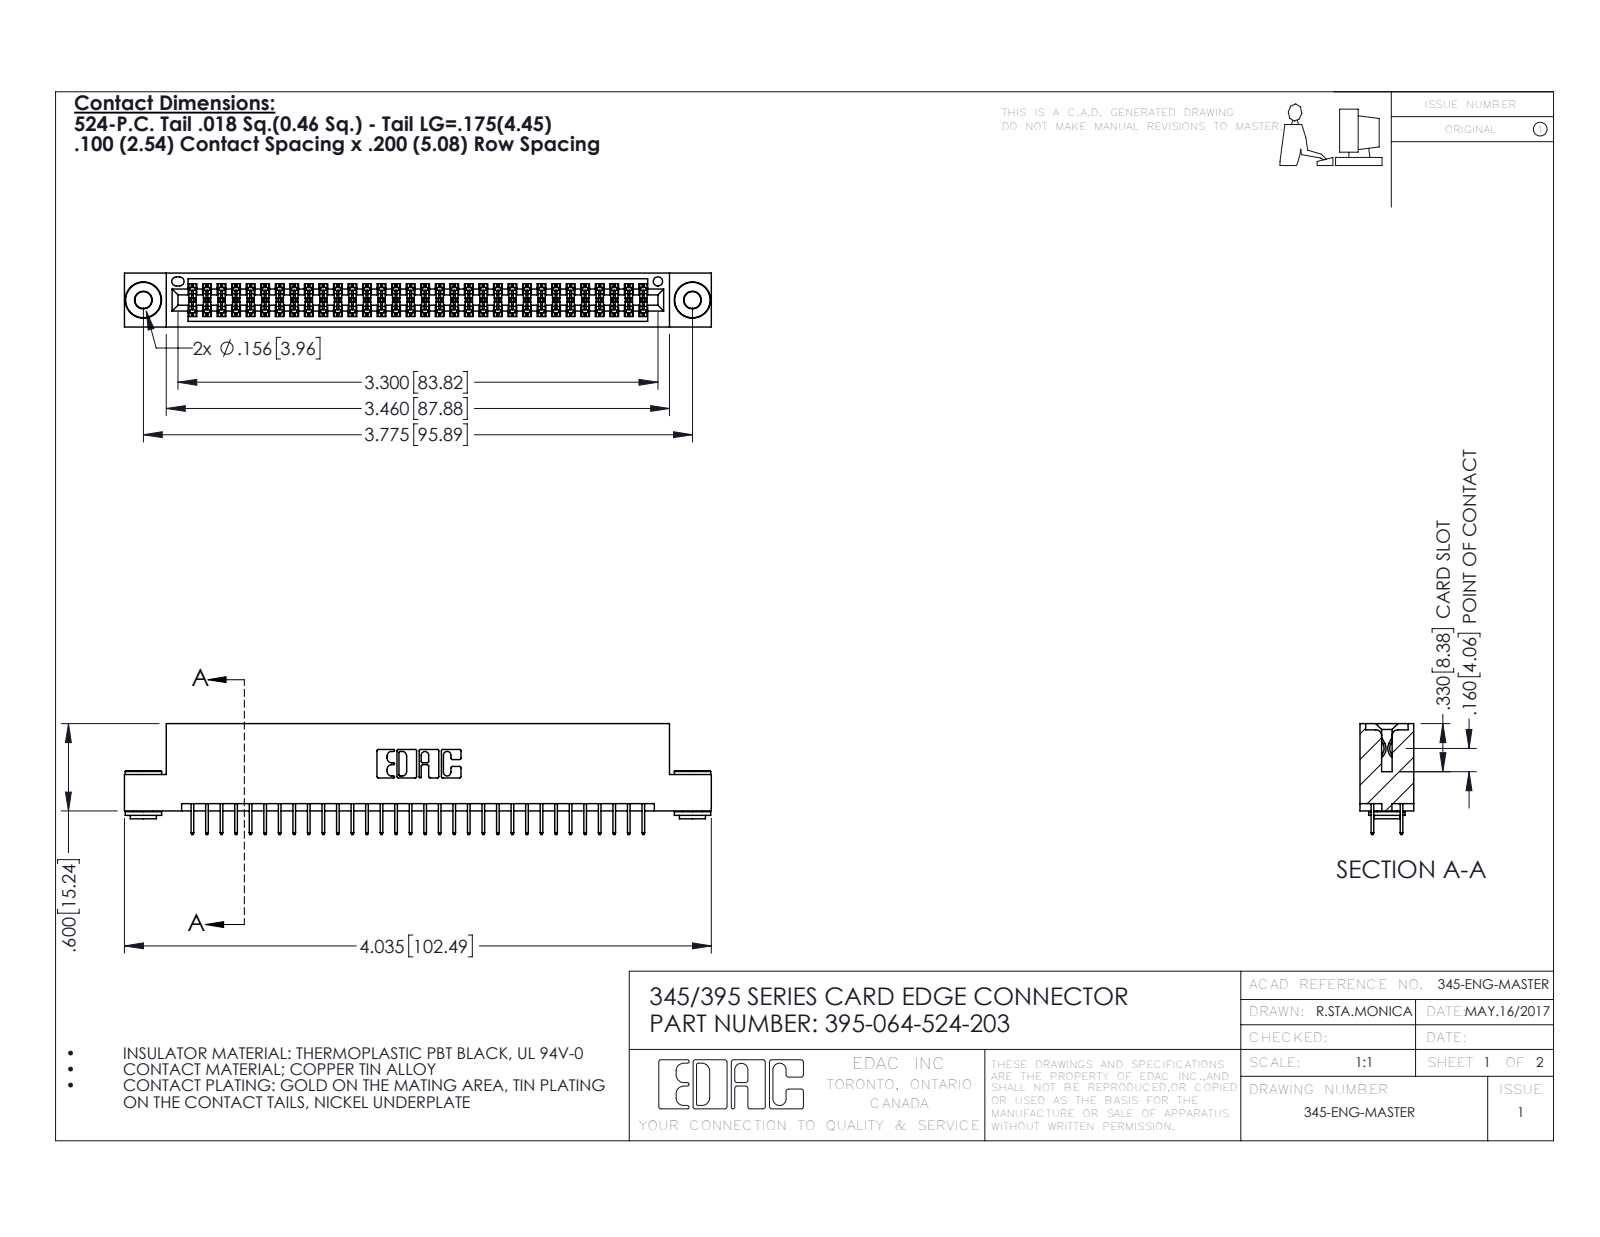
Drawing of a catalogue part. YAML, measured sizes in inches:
part_name: "345 Part_Flush Mounting Lugs - 0.156 Dia-TH; 345-250-002_345-250-002-102; 395-064-524-203; 345-292-001_345-293-124"
step_written_by: "SolidWorks 2016 (CONFIG_CONTROL_DESIGN)"
units: inches
bodies: {solids: 67, faces: 3620, planar: 2586, cylindrical: 1026, other: 8}
overall_size: [4.035, 0.762, 0.37]
volume: 0.597
surface_area: 22.04
round_holes:
  - {diameter: 0.116, count: 2}
  - {diameter: 0.156, count: 2}
  - {diameter: 0.064, count: 1}
round_bosses_or_shafts:
  - {diameter: 0.25, count: 2}
  - {diameter: 0.18, count: 2}
  - {diameter: 0.136, count: 2}
partial_cylinders:
  - {radius: 0.006, count: 96}
  - {radius: 0.01, count: 22}
  - {radius: 0.007, count: 6}
  - {radius: 0.031, count: 6}
  - {radius: 0.026, count: 3}
  - {radius: 0.014, count: 2}
  - {radius: 0.019, count: 2}
  - {radius: 0.022, count: 2}
face_to_face_distances: [0.072, 0.298, 0.2, 0.37, 0.025, 0.098, 0.272, 0.225, 0.072, 0.175]
hole_center_spacings: [0.27, 3.54, 3.775]
